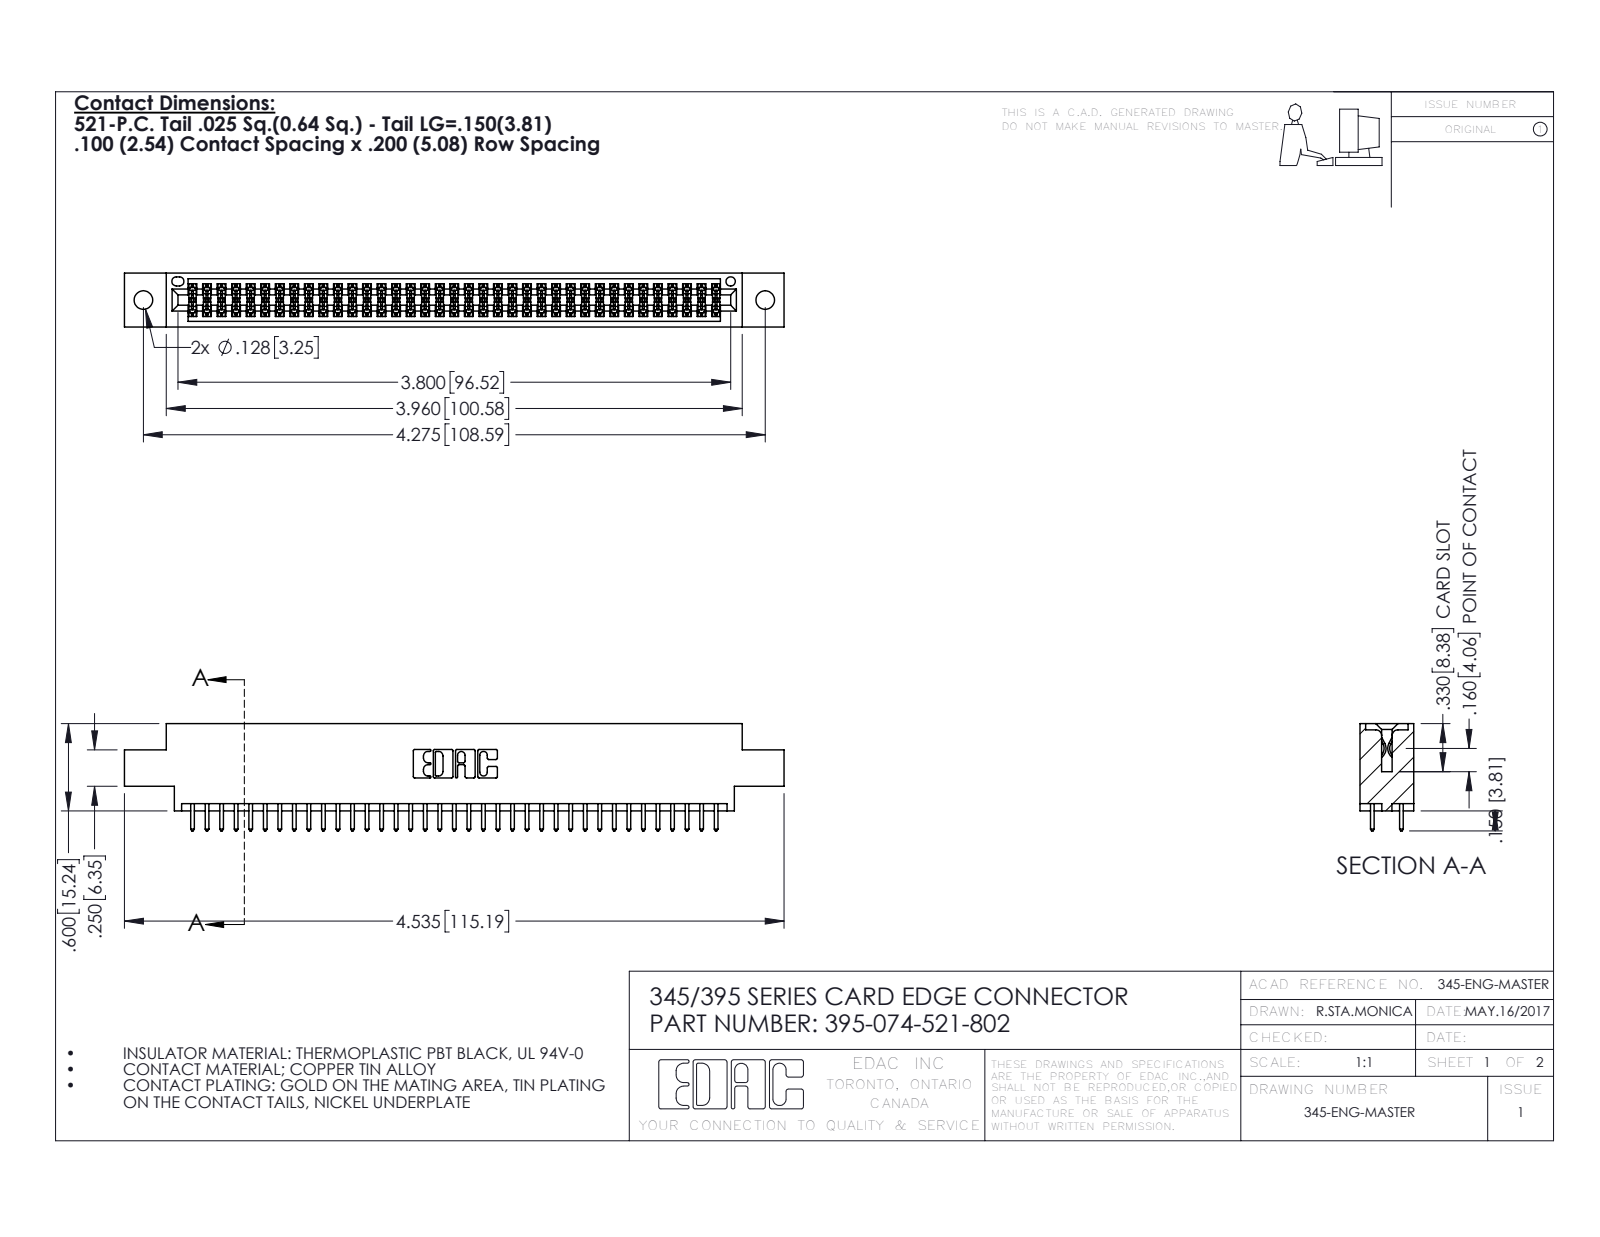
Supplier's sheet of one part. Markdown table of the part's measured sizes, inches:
| quantity | value |
| --- | --- |
| part name | 395-074-521-802; 345-292-001_345-293-121; 345 Part_0.170 Offset - 0.128 Dia |
| STEP written by | SolidWorks 2016 (CONFIG_CONTROL_DESIGN) |
| units | inches |
| bodies | 75 solids, 3830 faces (2526 planar, 1304 cylindrical, 0 other) |
| overall size | 4.535 × 0.737 × 0.37 |
| volume | 0.669 in³ |
| surface area | 24.46 in² |
| round holes (diameter × count) | 0.128 × 2, 0.064 × 1 |
| partial cylindrical surfaces (radius × count) | 0.006 × 111, 0.01 × 74, 0.01 × 22, 0.007 × 6, 0.031 × 6, 0.026 × 3, 0.014 × 2, 0.019 × 2 |
| main face-to-face distances | 0.298, 0.072, 0.37, 0.2, 0.098, 0.272, 0.025, 0.225, 0.175, 0.149 |
| hole center spacings | 0.27, 4.039, 4.275 |
